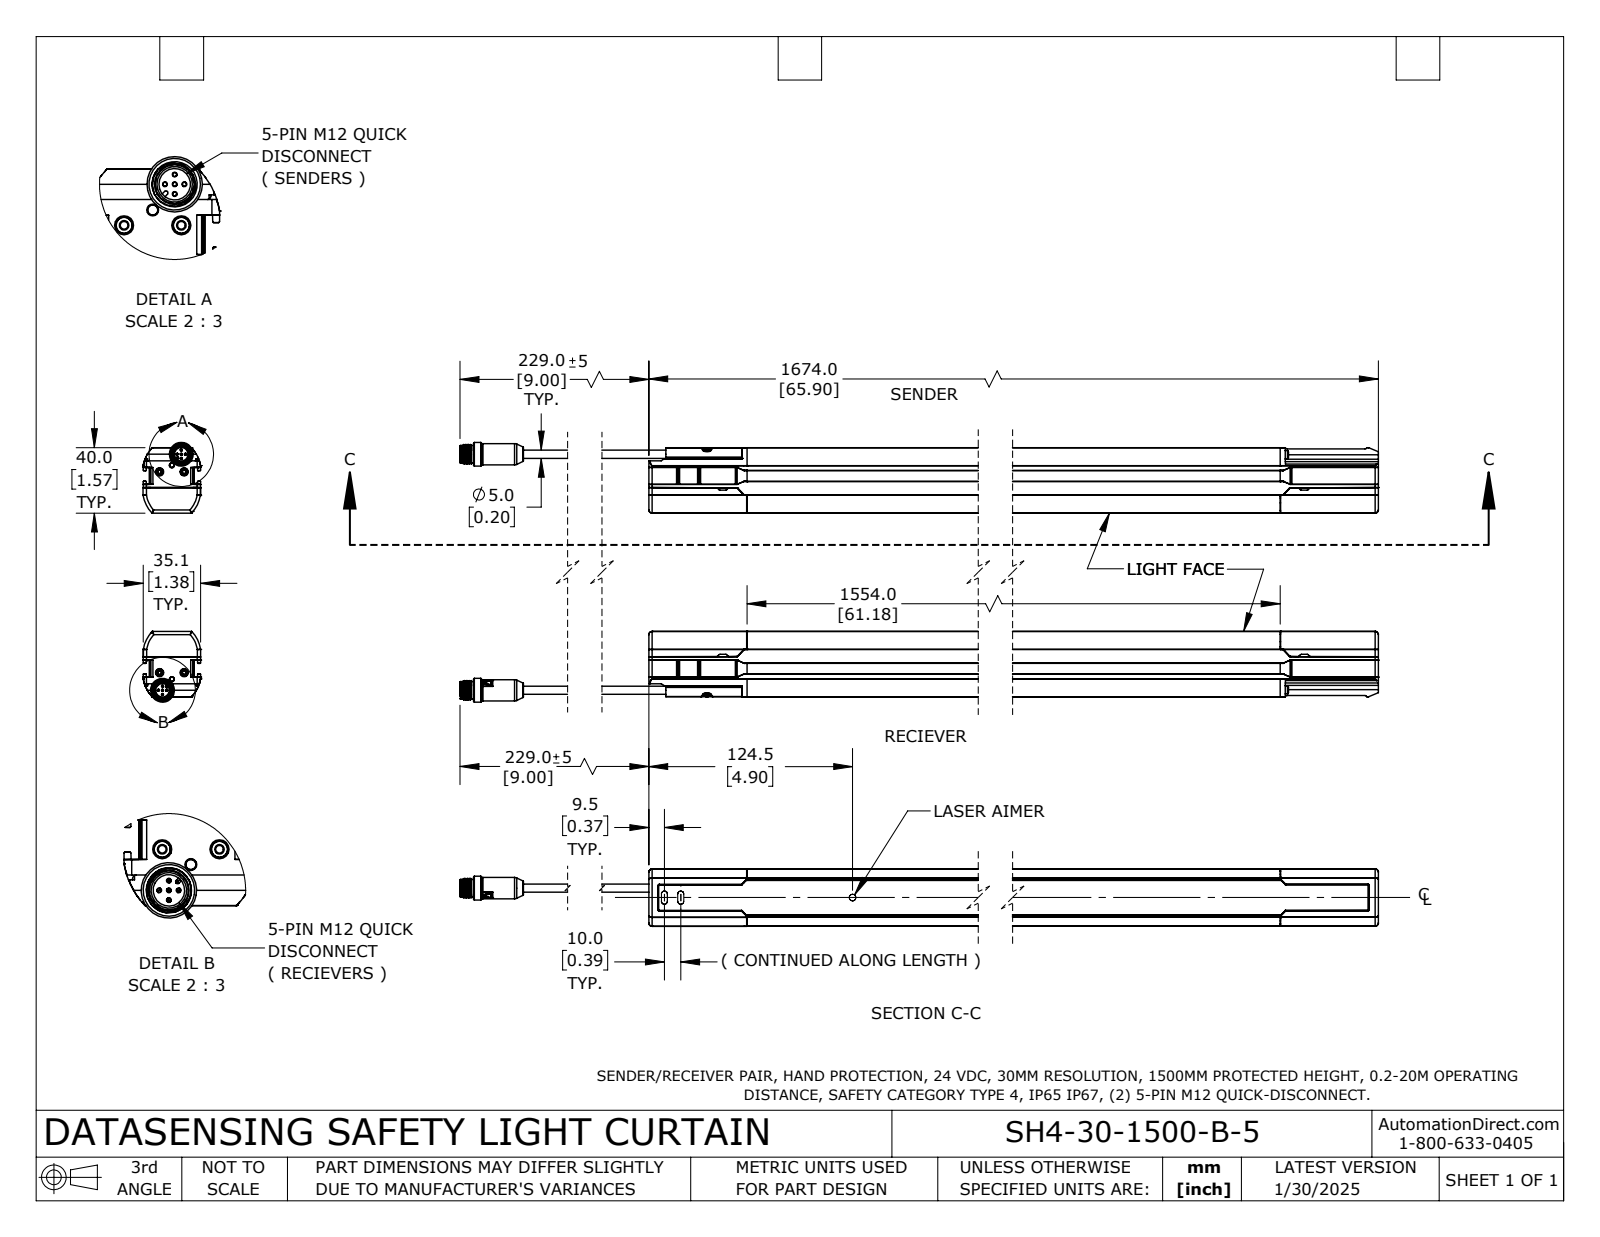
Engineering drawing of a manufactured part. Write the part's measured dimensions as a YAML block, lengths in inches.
part_name: "SH4-30-1500-B-5"
step_written_by: "SolidWorks 2024 (AUTOMOTIVE_DESIGN)"
units: inches
bodies: {solids: 4, faces: 2582, planar: 1178, cylindrical: 778, other: 626}
overall_size: [68.398, 6.248, 1.384]
volume: 217.6
surface_area: 917.3
round_holes:
  - {diameter: 0.079, count: 4}
  - {diameter: 0.118, count: 4}
  - {diameter: 0.197, count: 4}
  - {diameter: 0.1, count: 2}
  - {diameter: 0.1, count: 2}
  - {diameter: 0.101, count: 2}
  - {diameter: 0.101, count: 2}
  - {diameter: 0.11, count: 2}
  - {diameter: 0.325, count: 2}
  - {diameter: 0.382, count: 2}
  - {diameter: 0.407, count: 2}
  - {diameter: 0.425, count: 2}
round_bosses_or_shafts:
  - {diameter: 0.197, count: 10}
  - {diameter: 0.039, count: 10}
  - {diameter: 0.087, count: 8}
  - {diameter: 0.172, count: 4}
  - {diameter: 0.571, count: 2}
  - {diameter: 0.512, count: 2}
  - {diameter: 0.417, count: 2}
  - {diameter: 0.374, count: 2}
partial_cylinders:
  - {radius: 0.01, count: 164}
  - {radius: 0.016, count: 66}
  - {radius: 0.02, count: 50}
  - {radius: 0.008, count: 36}
  - {radius: 0.031, count: 20}
  - {radius: 0.031, count: 12}
  - {radius: 0.079, count: 12}
  - {radius: 0.059, count: 10}
face_to_face_distances: [1.496, 4.496, 0.156, 1.222, 3, 5.992, 1.378, 1.067, 4.634, 0.069]
hole_center_spacings: [0.866, 5.163, 5.235, 0.429, 0.591, 0.672, 4.831, 4.867]
